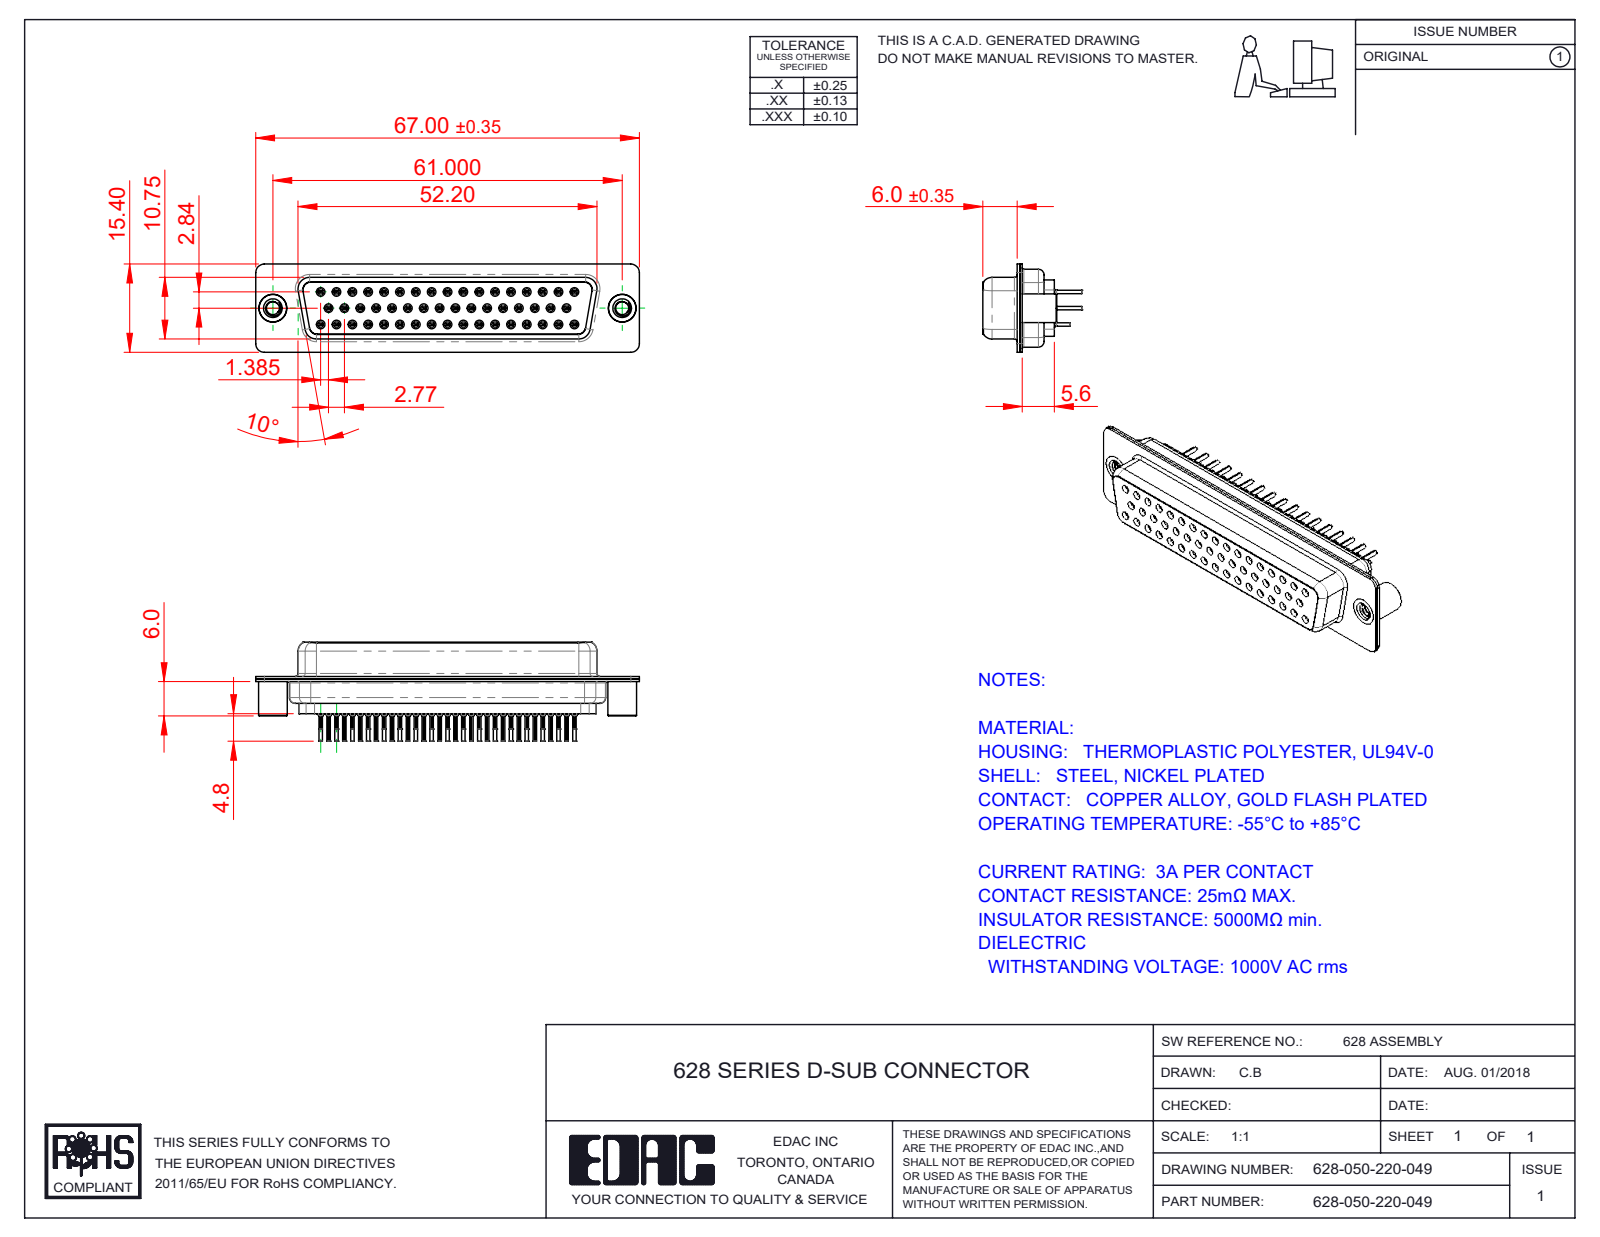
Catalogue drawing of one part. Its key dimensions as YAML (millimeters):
part_name: "628 Contact Row 3_20L; 628 Contact Row 1_20L; 628 4-40 Threaded Standoff BS; 628 Shell Front_50 Contacts (+4 more)"
step_written_by: "SolidWorks 2020 (CONFIG_CONTROL_DESIGN)"
units: millimeters
bodies: {solids: 55, faces: 6651, planar: 1617, cylindrical: 1807, other: 3227}
overall_size: [67, 17.3, 15.4]
volume: 6818
surface_area: 15466
round_holes:
  - {diameter: 0.2, count: 50}
  - {diameter: 0.8, count: 50}
  - {diameter: 0.9, count: 50}
  - {diameter: 1.1, count: 50}
  - {diameter: 1.6, count: 50}
  - {diameter: 1.7, count: 17}
  - {diameter: 2.26, count: 2}
  - {diameter: 4, count: 2}
  - {diameter: 4.05, count: 2}
  - {diameter: 4.85, count: 2}
round_bosses_or_shafts:
  - {diameter: 2, count: 50}
  - {diameter: 1.5, count: 50}
  - {diameter: 1.2, count: 50}
  - {diameter: 0.6, count: 50}
  - {diameter: 5, count: 2}
  - {diameter: 4.95, count: 2}
  - {diameter: 4.8, count: 2}
partial_cylinders:
  - {radius: 0.1, count: 100}
  - {radius: 0.28, count: 33}
  - {radius: 1.5, count: 16}
  - {radius: 2, count: 12}
  - {radius: 1.35, count: 8}
  - {radius: 0.25, count: 4}
  - {radius: 0.5, count: 4}
  - {radius: 0.6, count: 4}
face_to_face_distances: [0.45, 0.4, 11.33, 1.87, 10.3, 6.5, 0.9, 6.05, 6.45, 6]
hole_center_spacings: [3.16, 2.77, 5.54, 8.31, 11.08, 13.85, 16.62, 19.39]
